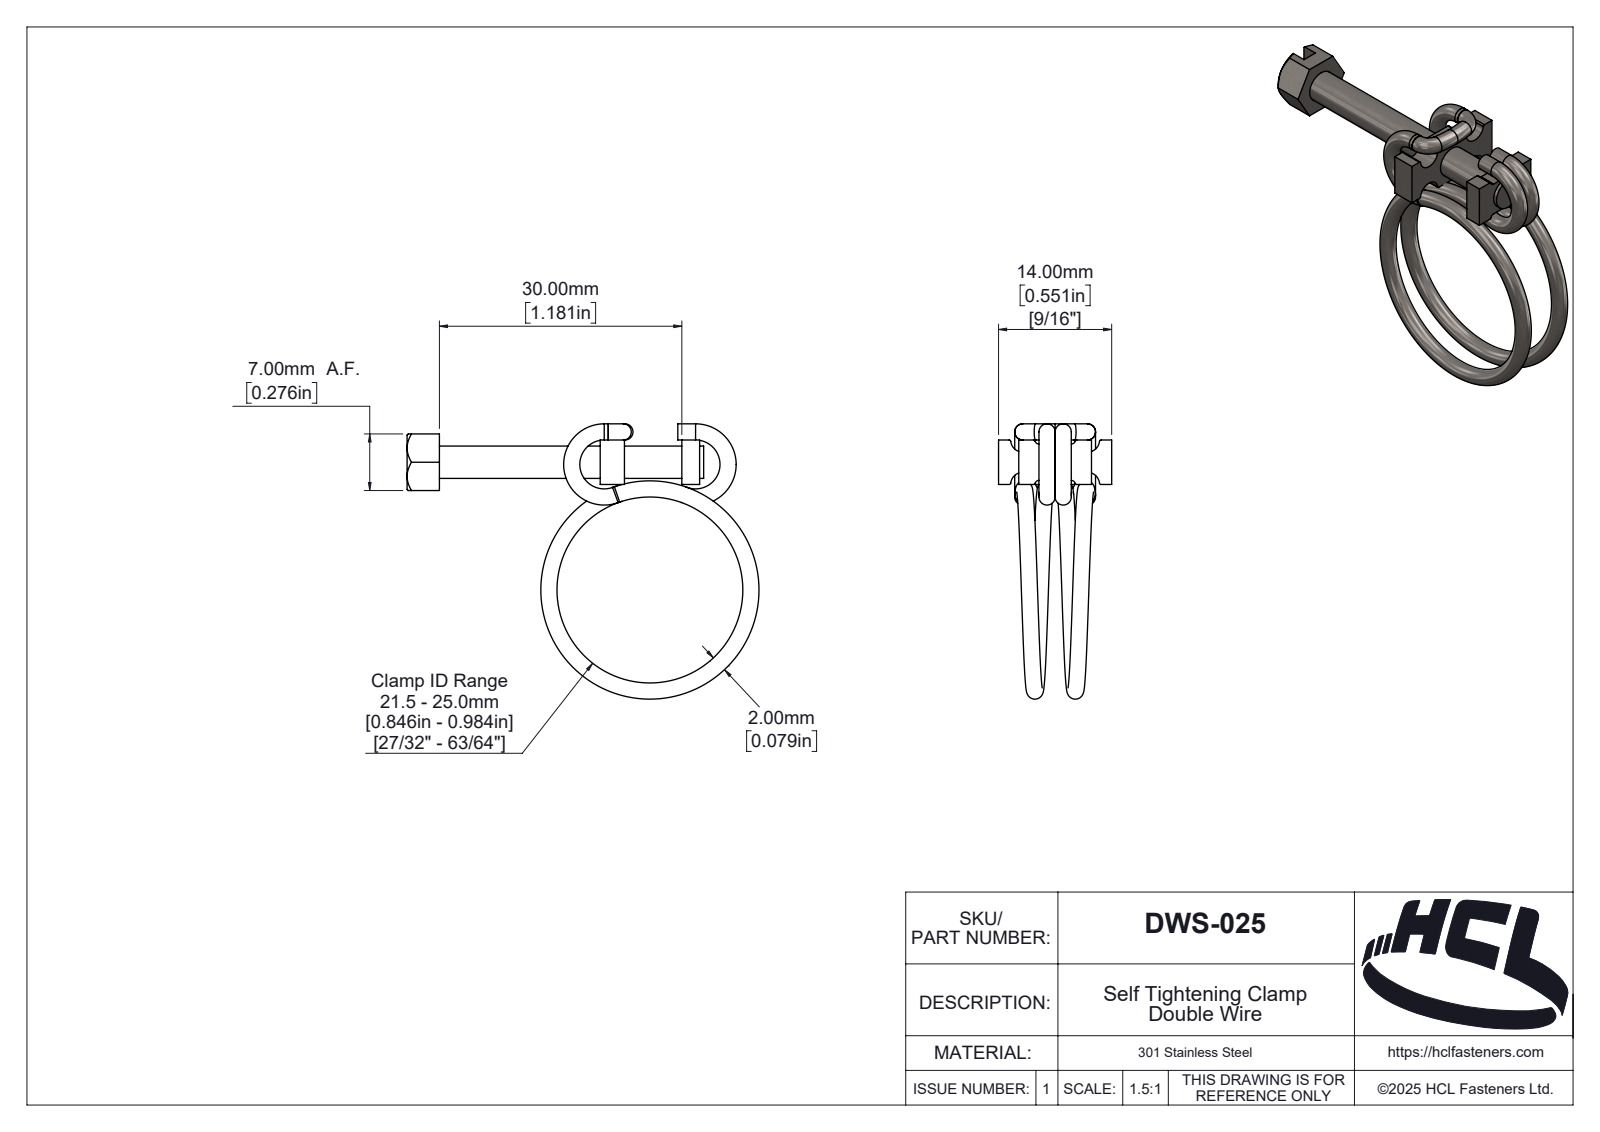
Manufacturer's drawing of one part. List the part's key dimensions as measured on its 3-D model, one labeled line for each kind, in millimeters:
Part name (STEP PRODUCT): DWS-025
STEP written by: SolidWorks 2025 (AUTOMOTIVE_DESIGN)
Units: millimetres
Bodies: 6 solids, 209 faces (51 planar, 74 cylindrical, 84 other)
Overall size (bounding box): 43.55 × 34.05 × 14
Volume: 1 548 mm³ · Surface area: 2 609 mm²
Round holes (diameter × count): ⌀4 ×1
Round bosses / shafts (diameter × count): ⌀2 ×4
Partial cylindrical surfaces — rounded edges, fillets, slot ends (radius × count): R0.2 ×12, R0.5 ×4, R1.5 ×4, R0.4 ×1, R0.51 ×1, R0.53 ×1, R0.64 ×1, R0.91 ×1
Main face-to-face distances: 2, 5.5, 3, 22.9, 7, 0.5, 10.1, 7.1, 12.3, 9.3
